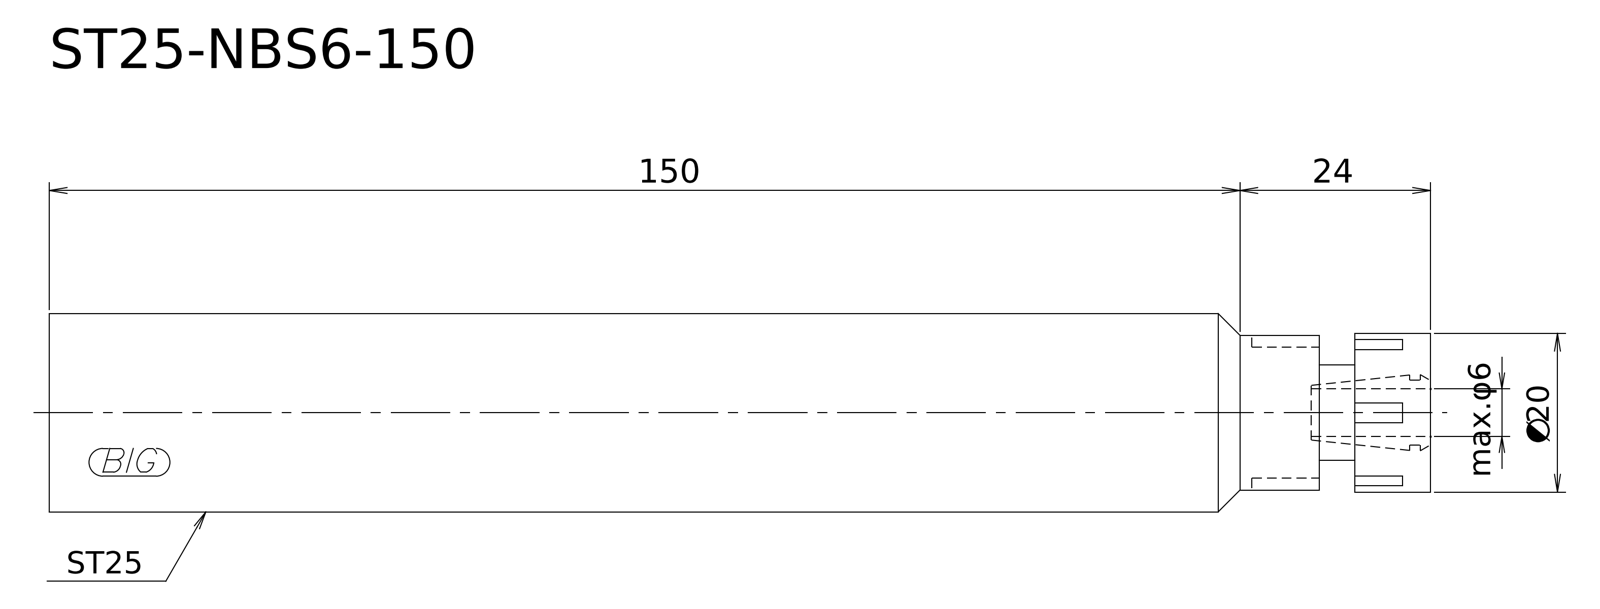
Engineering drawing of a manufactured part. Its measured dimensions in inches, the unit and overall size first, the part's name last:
Units: inches
Overall size (bounding box): 6.85 × 0.984 × 0.984
Round bosses / shafts (diameter × count): ⌀0.984 ×1, ⌀0.787 ×1, ⌀0.768 ×1, ⌀0.472 ×1
Main face-to-face distances: 6.85, 0.374, 6.476, 0.551, 0.177, 6.299
Volume: 4.872 in³ · Surface area: 22.33 in²
Bodies: 1 solid, 9 faces (4 planar, 4 cylindrical, 1 other)
STEP written by: Kubotek KeyCreator V8.5.1 (14335) (CONFIG_CONTROL_DESIGN)
